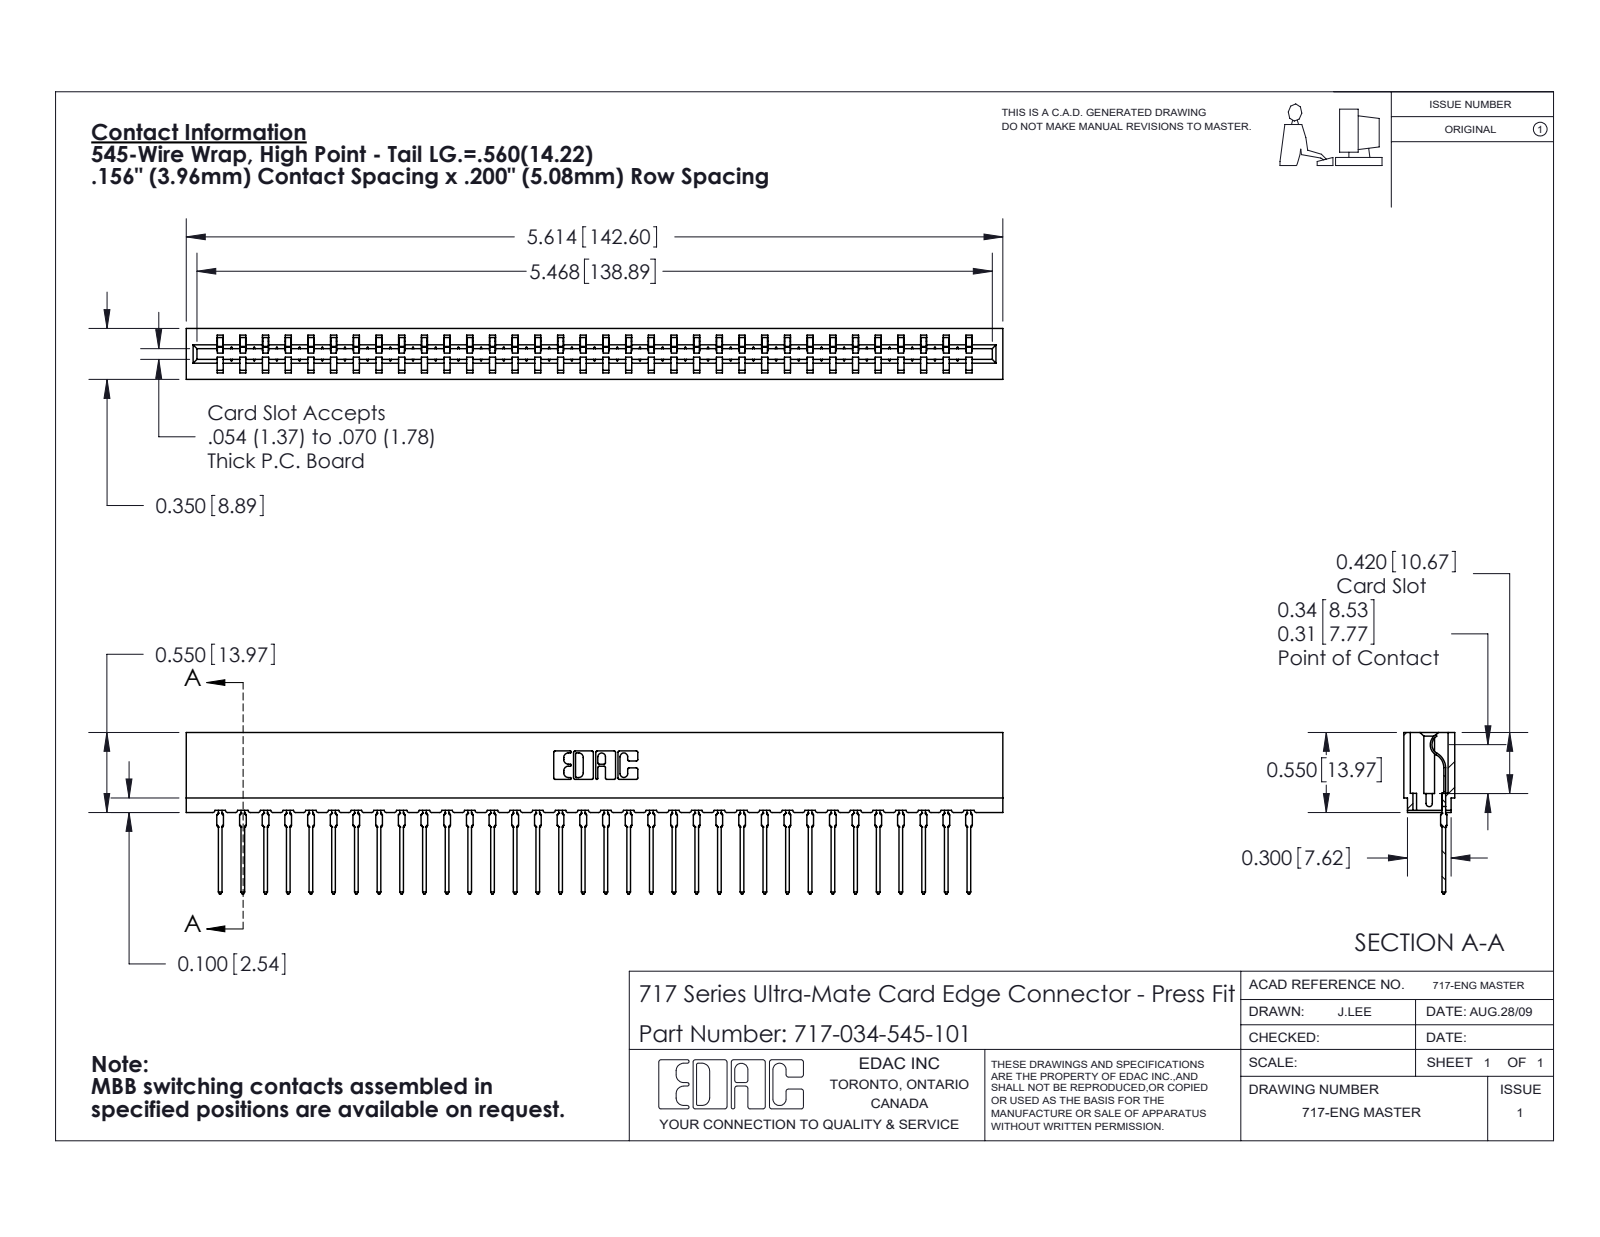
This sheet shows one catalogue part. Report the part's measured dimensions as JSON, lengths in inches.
{"part_name": "745-292-001_545; 717-034-545-101; 717 Part_Insulator Option - 06", "step_written_by": "SolidWorks 2020 (CONFIG_CONTROL_DESIGN)", "units": "inches", "bodies": {"solids": 35, "faces": 3936, "planar": 2366, "cylindrical": 686, "other": 884}, "overall_size": [5.614, 1.109, 0.35], "volume_in3": 0.743, "surface_area_in2": 27.19, "partial_cylinders_radius": [[0.015, 68], [0.021, 68], [0.01, 22], [0.007, 6], [0.031, 6], [0.005, 4], [0.011, 4], [0.026, 3]], "face_to_face_distances": [0.212, 0.138, 0.35, 0.063, 0.287, 0.076, 0.149, 0.074, 0.156, 0.045]}
